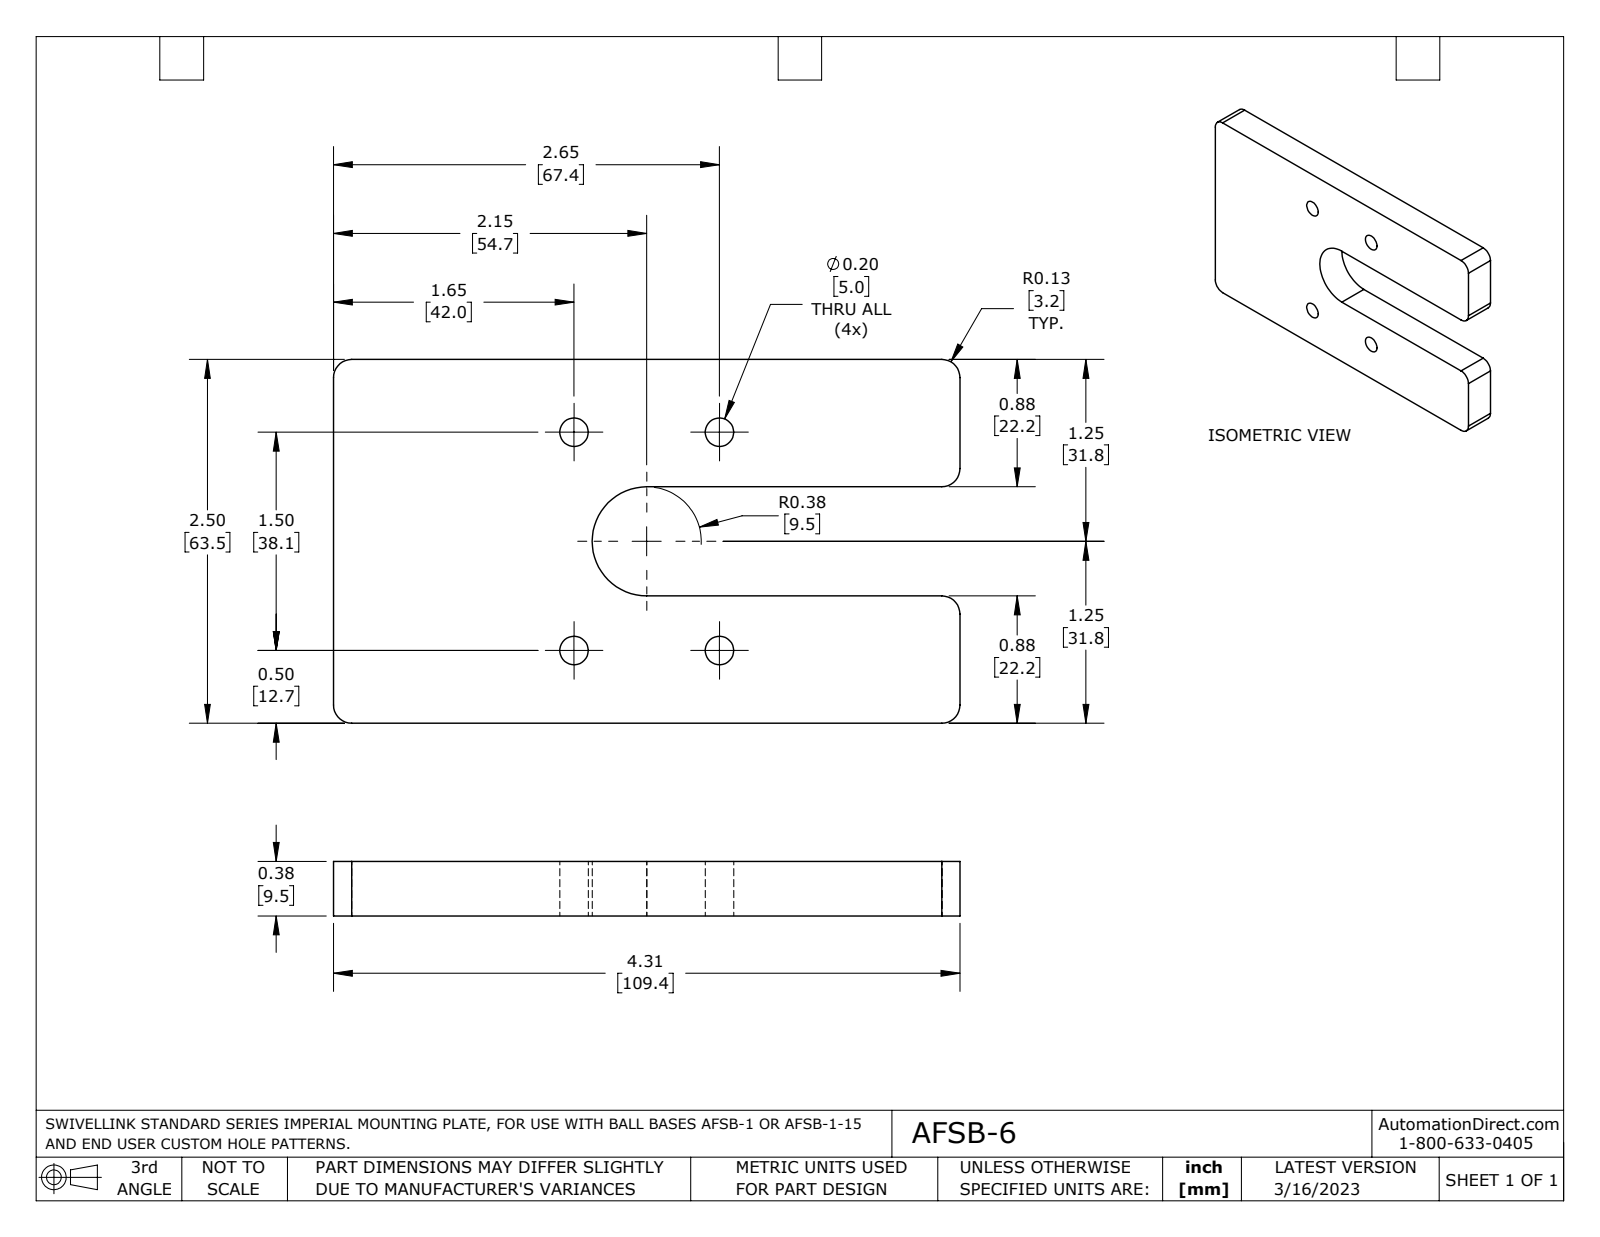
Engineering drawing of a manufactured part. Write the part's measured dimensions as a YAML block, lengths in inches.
part_name: "AFSB-6"
step_written_by: "SolidWorks 2021 (AUTOMOTIVE_DESIGN)"
units: inches
bodies: {solids: 1, faces: 20, planar: 9, cylindrical: 11, other: 0}
overall_size: [4.307, 2.5, 0.375]
volume: 3.297
surface_area: 25.27
round_holes:
  - {diameter: 0.196, count: 4}
partial_cylinders:
  - {radius: 0.125, count: 6}
  - {radius: 0.375, count: 1}
face_to_face_distances: [0.375, 0.875, 1.625, 2.5, 0.75, 4.307]
hole_center_spacings: [1, 1.5, 1.803]
